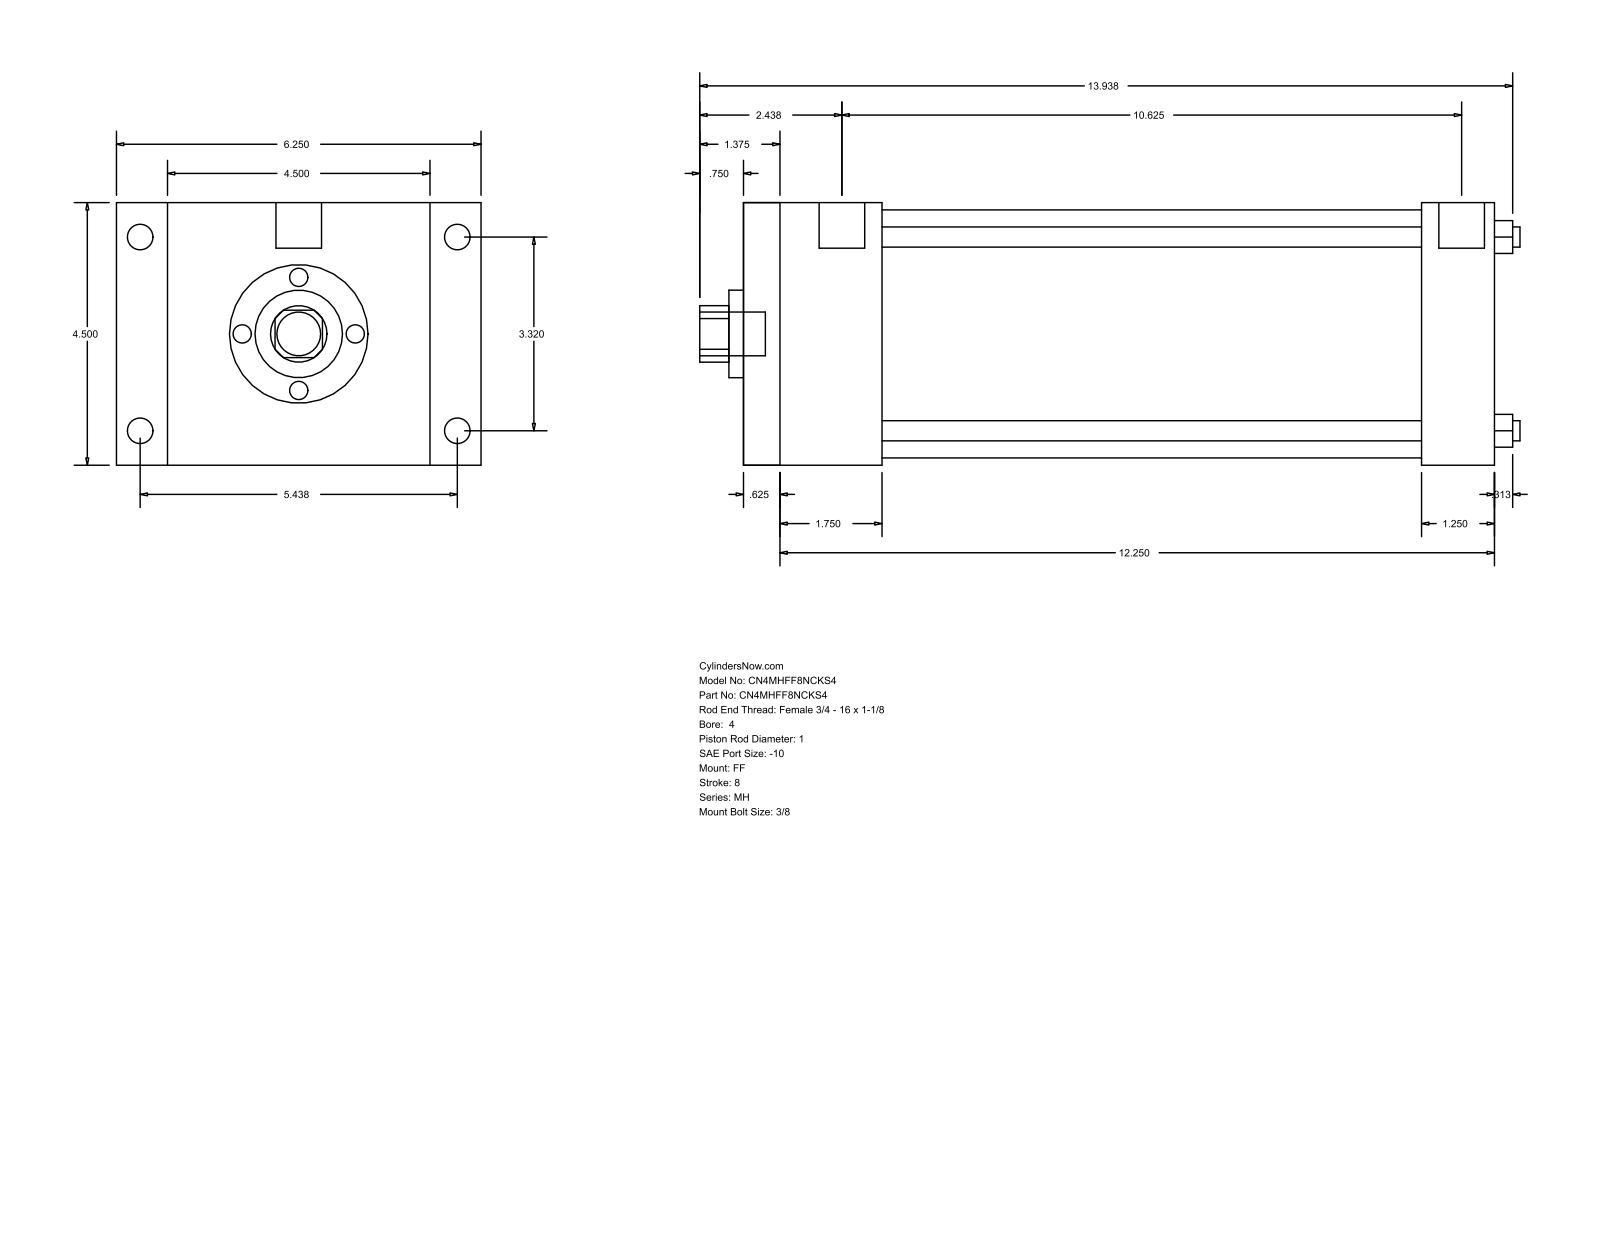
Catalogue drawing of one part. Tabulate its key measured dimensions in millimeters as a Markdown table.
| quantity | value |
| --- | --- |
| part name | MH_FF__0400_1 |
| STEP written by | GSSL Pune (CONFIG_CONTROL_DESIGN) |
| units | millimeters |
| bodies | 0 solids, 92 faces (64 planar, 28 cylindrical, 0 other) |
| overall size | 357.19 × 158.75 × 114.3 |
| round holes (diameter × count) | 8.76 × 4, 25.4 × 1, 38.1 × 1, 107.95 × 1 |
| round bosses / shafts (diameter × count) | 11.13 × 4, 8.73 × 4, 19.84 × 2, 19.05 × 1 |
| partial cylindrical surfaces (radius × count) | 12.29 × 1 |
| main face-to-face distances | 114.3, 327.02, 15.87, 311.15, 60.33, 44.46, 266.69, 295.27, 279.4, 234.94 |
| hole center spacings | 59.62, 84.32, 119.25 |
